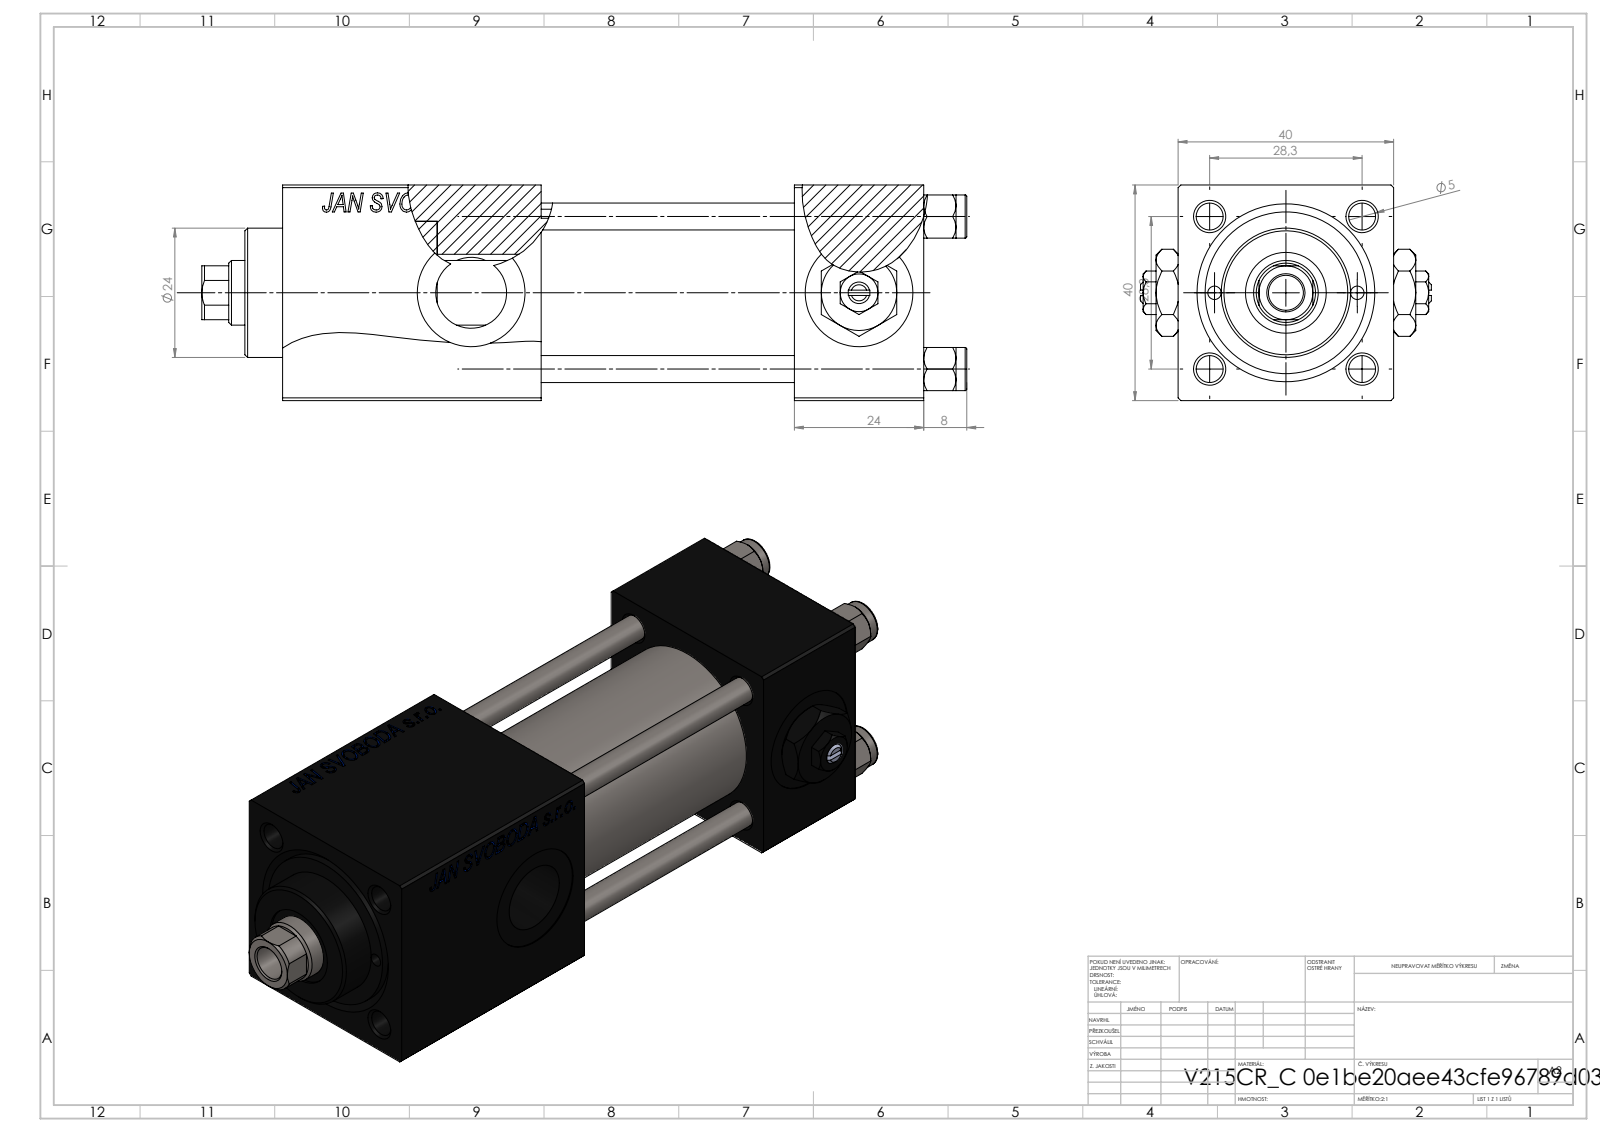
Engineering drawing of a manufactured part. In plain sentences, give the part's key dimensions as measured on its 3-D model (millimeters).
The part is named "V215CR_C_TYCINKA; V215_VC_A; V215CR_C_Body; NUT_M5_C (+2 more)". Its 3-D file was written by "SolidWorks 2019 (CONFIG_CONTROL_DESIGN)". It is 13 solids with 1254 faces: 574 planar, 102 cylindrical and 578 other. Overall it measures 142 by 54 by 40 millimeters. Its volume is 140 936 cubic millimeters and its surface area 56 288 square millimeters. Round holes: 4 of diameter 5, 3 of diameter 20, 2 of diameter 2.5, 2 of diameter 7, 2 of diameter 13.16, 1 of diameter 6.5, 1 of diameter 12, 1 of diameter 15, 1 of diameter 25, 1 of diameter 30. Round bosses or shafts: 4 of diameter 8, 1 of diameter 31, 1 of diameter 24. Partial cylindrical surfaces (rounded edges, fillets, slot ends): 1 of radius 5.5. The main face-to-face distances are 40, 24, 39.8, 90.3, 66.3, 47, 48, 71, 19.3, 95. The hole center spacings are 14.18, 20.01, 28.3, 30.84, 13.25, 40.02, 26.5, 72.
